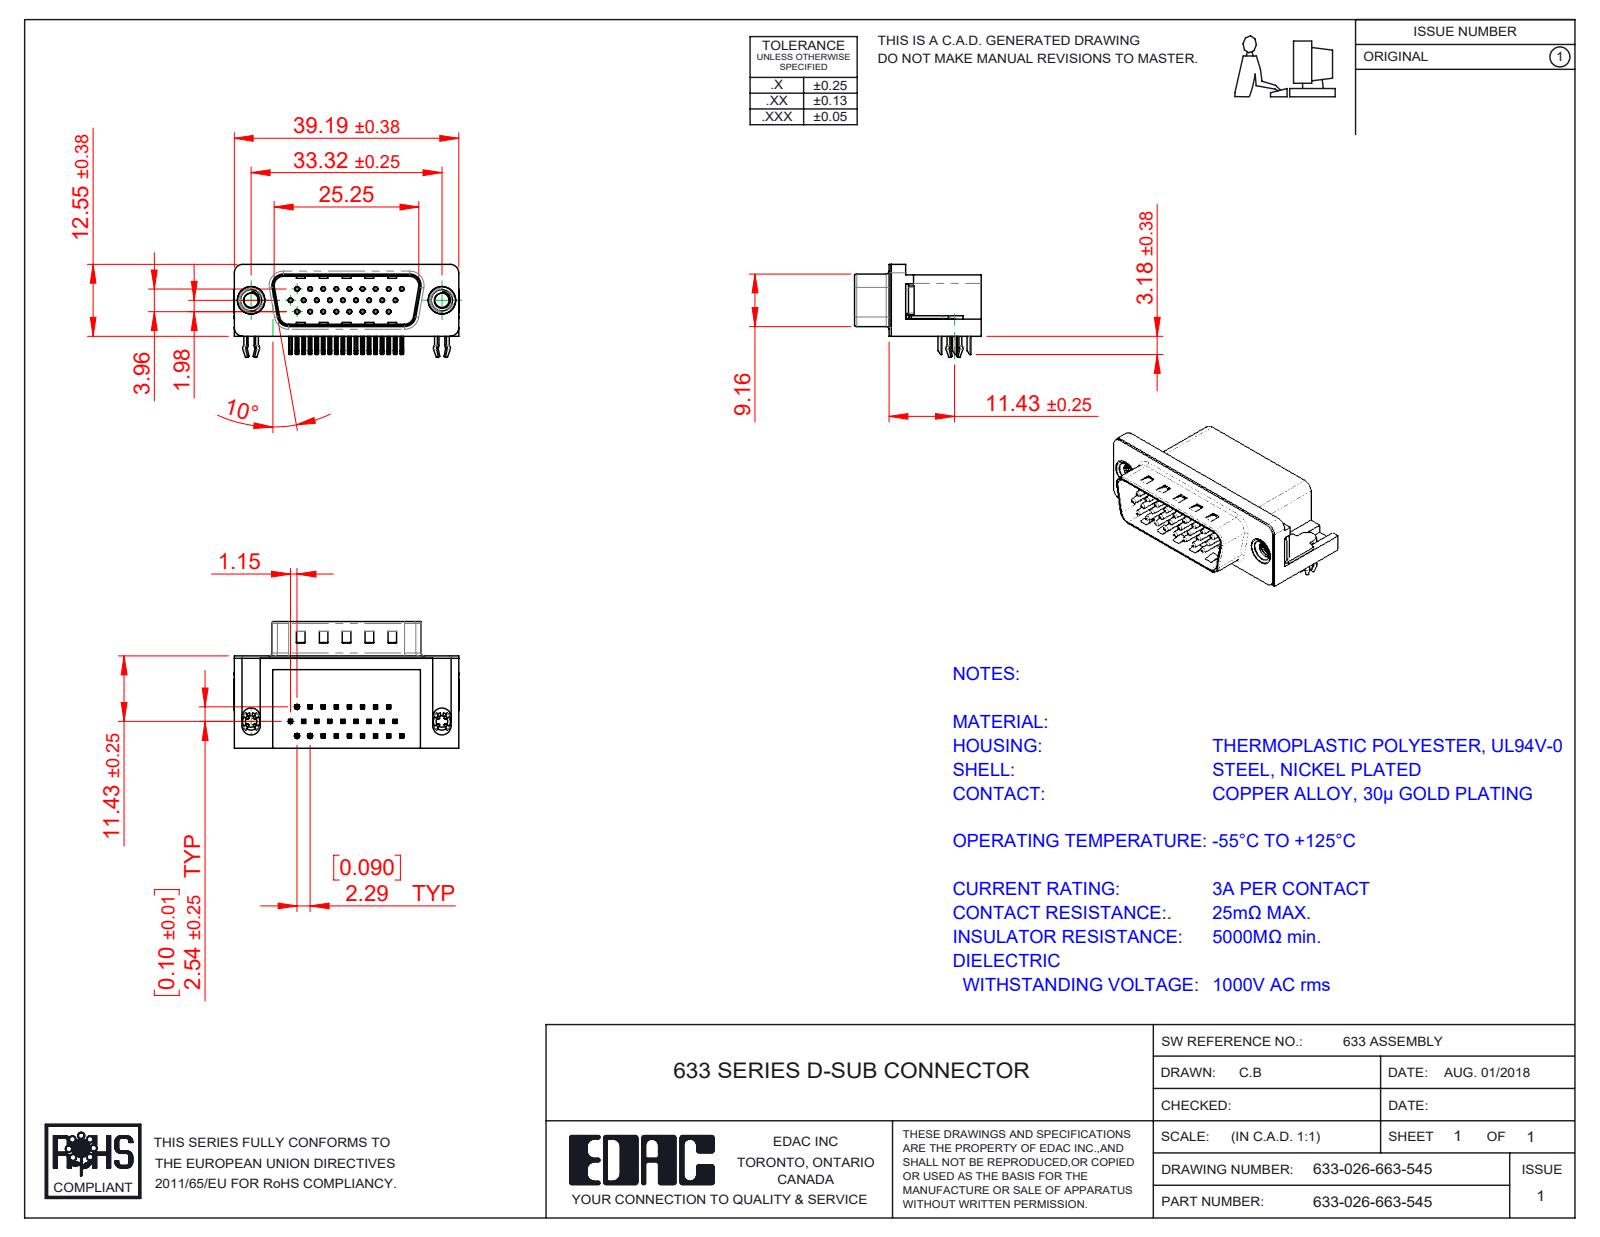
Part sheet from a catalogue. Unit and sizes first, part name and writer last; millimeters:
Units: millimetres
Overall size (bounding box): 39.22 × 22.1 × 16.25
Round holes (diameter × count): ⌀0.35 ×26, ⌀0.8 ×26, ⌀2 ×2, ⌀2.5 ×2, ⌀4 ×2, ⌀4.8 ×2, ⌀5 ×2
Round bosses / shafts (diameter × count): ⌀0.75 ×26, ⌀4.9 ×2, ⌀4.75 ×2, ⌀3.9 ×2, ⌀3 ×2
Partial cylindrical surfaces — rounded edges, fillets, slot ends (radius × count): R0.25 ×116, R0.12 ×52, R1 ×16, R0.5 ×9, R1.5 ×8, R1.6 ×8, R0.9 ×4, R2 ×4
Main face-to-face distances: 0.4, 10.35, 15.7, 2.9, 2.5, 16.1, 8.76, 0.35, 10.7, 0.5
Hole centre spacings: 2.29, 4.57, 2.28, 3.96, 6.05, 4.58, 6.86, 7.92
Volume: 5 602 mm³ · Surface area: 7 328 mm²
Bodies: 32 solids, 2424 faces (1463 planar, 688 cylindrical, 273 other)
Part name (STEP PRODUCT): 633-026-663-545; 633 Contact Bottom; 633 M3 Threaded Rivet; 633 Contact Middle (+4 more)
STEP written by: SolidWorks 2016 (CONFIG_CONTROL_DESIGN)
